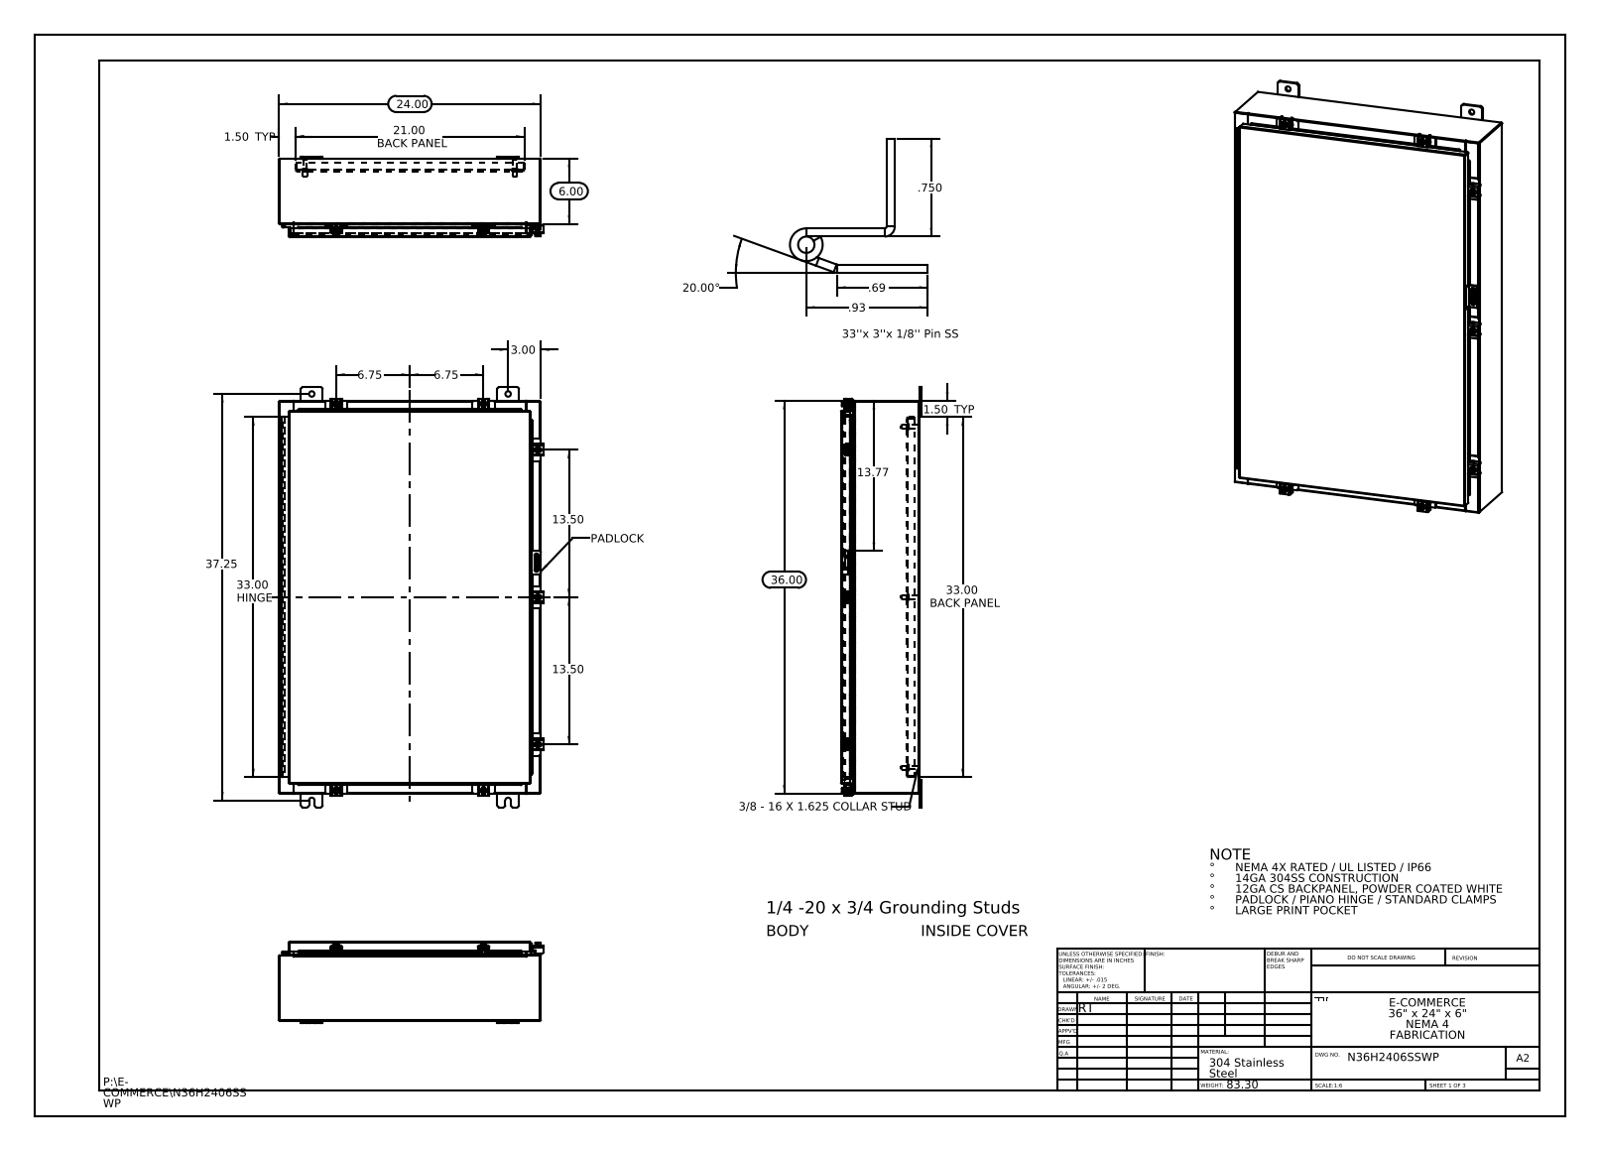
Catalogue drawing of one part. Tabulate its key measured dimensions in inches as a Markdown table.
| quantity | value |
| --- | --- |
| part name | N36H2406SSWP 22101002; N36H2406SSWP Mounting Studs; N36H2406SSWP Standard Clamps; N36H2406SSWP Hinge Enclosure Side2 (+8 more) |
| STEP written by | SolidWorks 2013 (CONFIG_CONTROL_DESIGN) |
| units | inches |
| bodies | 54 solids, 2184 faces (1138 planar, 922 cylindrical, 124 other) |
| overall size | 38.5 × 24.211 × 7.389 |
| volume | 292.8 in³ |
| surface area | 7 268 in² |
| round holes (diameter × count) | 0.5 × 10, 0.213 × 7, 0.26 × 7, 0.125 × 2, 0.125 × 1 |
| round bosses / shafts (diameter × count) | 0.25 × 8, 0.5 × 7, 0.399 × 7, 0.625 × 6, 0.375 × 6, 0.33 × 6 |
| partial cylindrical surfaces (radius × count) | 0.06 × 34, 0.013 × 27, 0.19 × 24, 0.088 × 21, 0.12 × 14, 0.141 × 14, 0.05 × 11, 0.08 × 10 |
| main face-to-face distances | 0.075, 7.126, 7.201, 7.051, 0.104, 1, 1.075, 6.051, 6.126, 1.179 |
| hole center spacings | 13.5, 15.625, 17.957, 24.793, 33.474, 37.154, 19.25, 1.858 |
